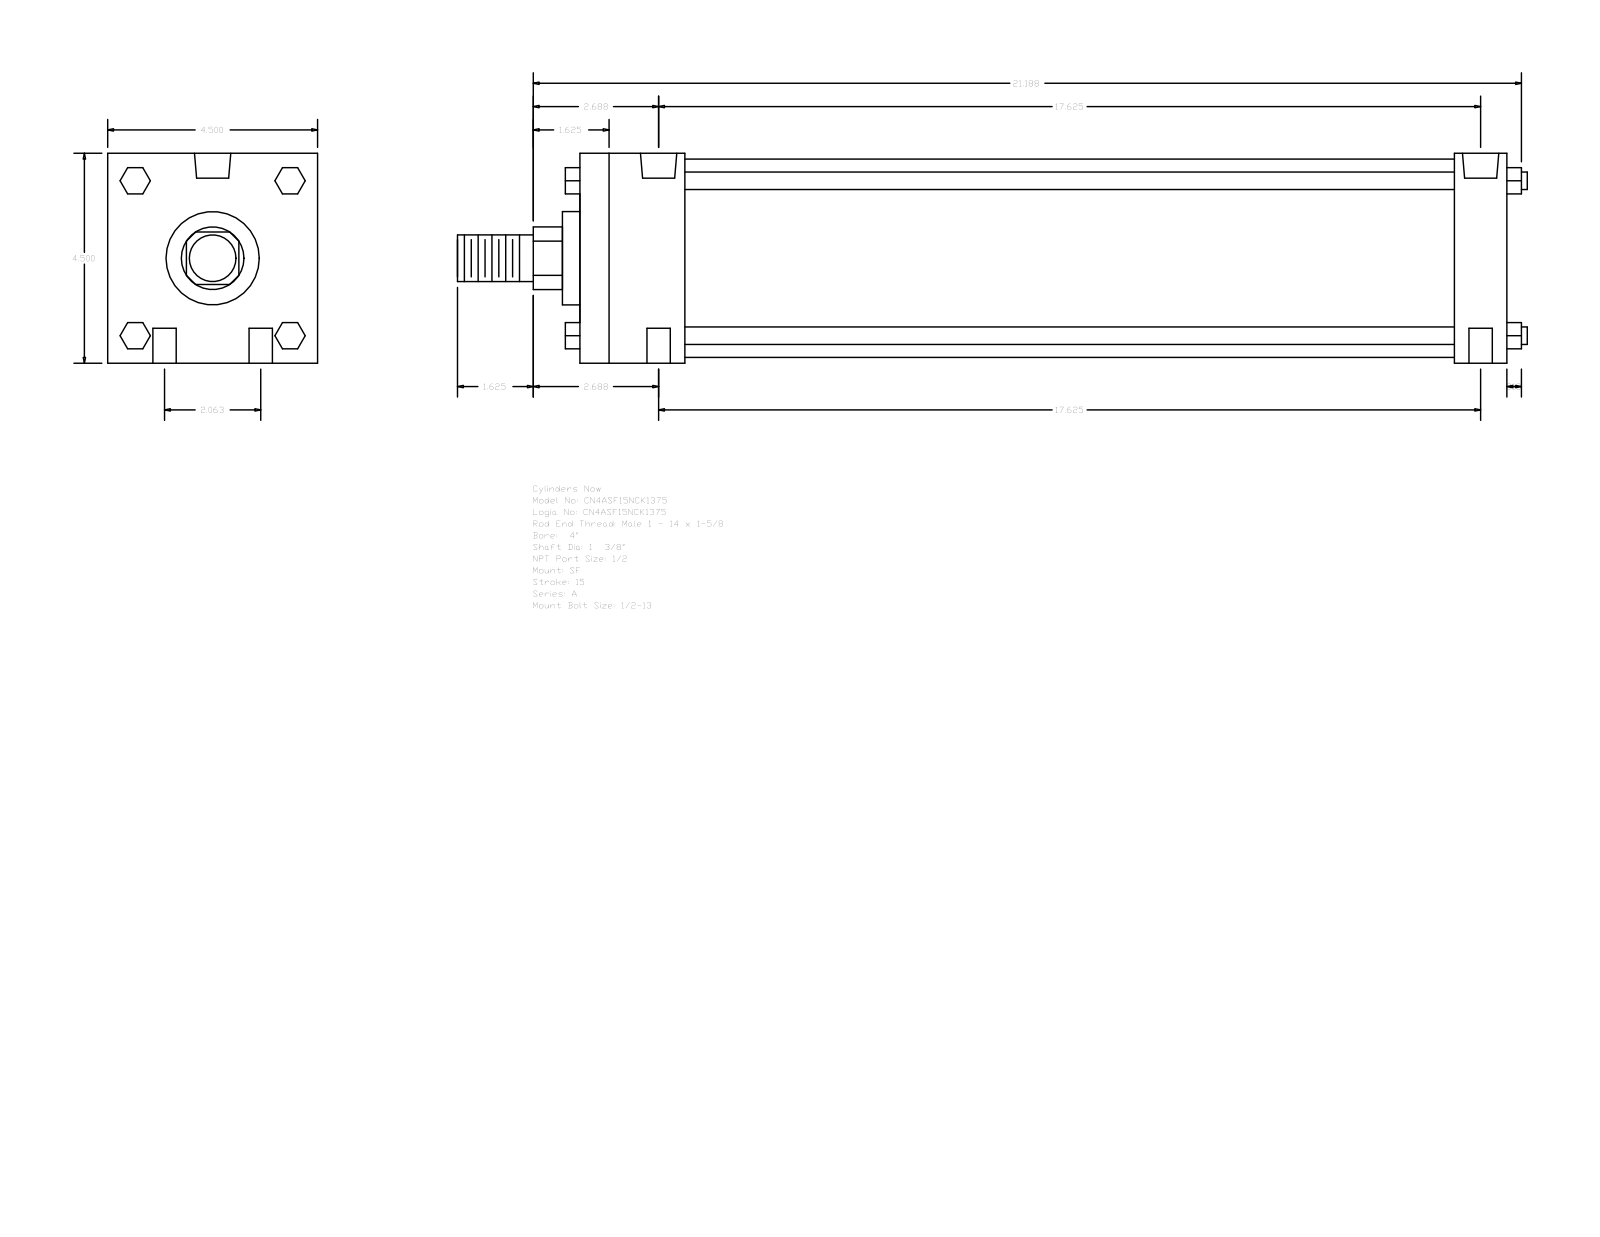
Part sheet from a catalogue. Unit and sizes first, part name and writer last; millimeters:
Units: millimetres
Overall size (bounding box): 582.61 × 114.3 × 114.3
Round holes (diameter × count): ⌀12.7 ×4, ⌀8.73 ×2, ⌀19.77 ×2
Round bosses / shafts (diameter × count): ⌀9.53 ×4, ⌀107.95 ×1, ⌀50.8 ×1, ⌀34.92 ×1, ⌀25.4 ×1
Partial cylindrical surfaces — rounded edges, fillets, slot ends (radius × count): R17.06 ×1
Main face-to-face distances: 114.3, 504.83, 57.15, 28.58, 476.25, 419.1, 447.68, 66.67, 14.29, 9.52
Hole centre spacings: 26.19, 448.45, 447.68, 52.38, 450.73, 441.32
Bodies: 0 solids, 124 faces (94 planar, 30 cylindrical, 0 other)
Part name (STEP PRODUCT): A_SF__0400_1.375
STEP written by: GSSL Pune (CONFIG_CONTROL_DESIGN)
